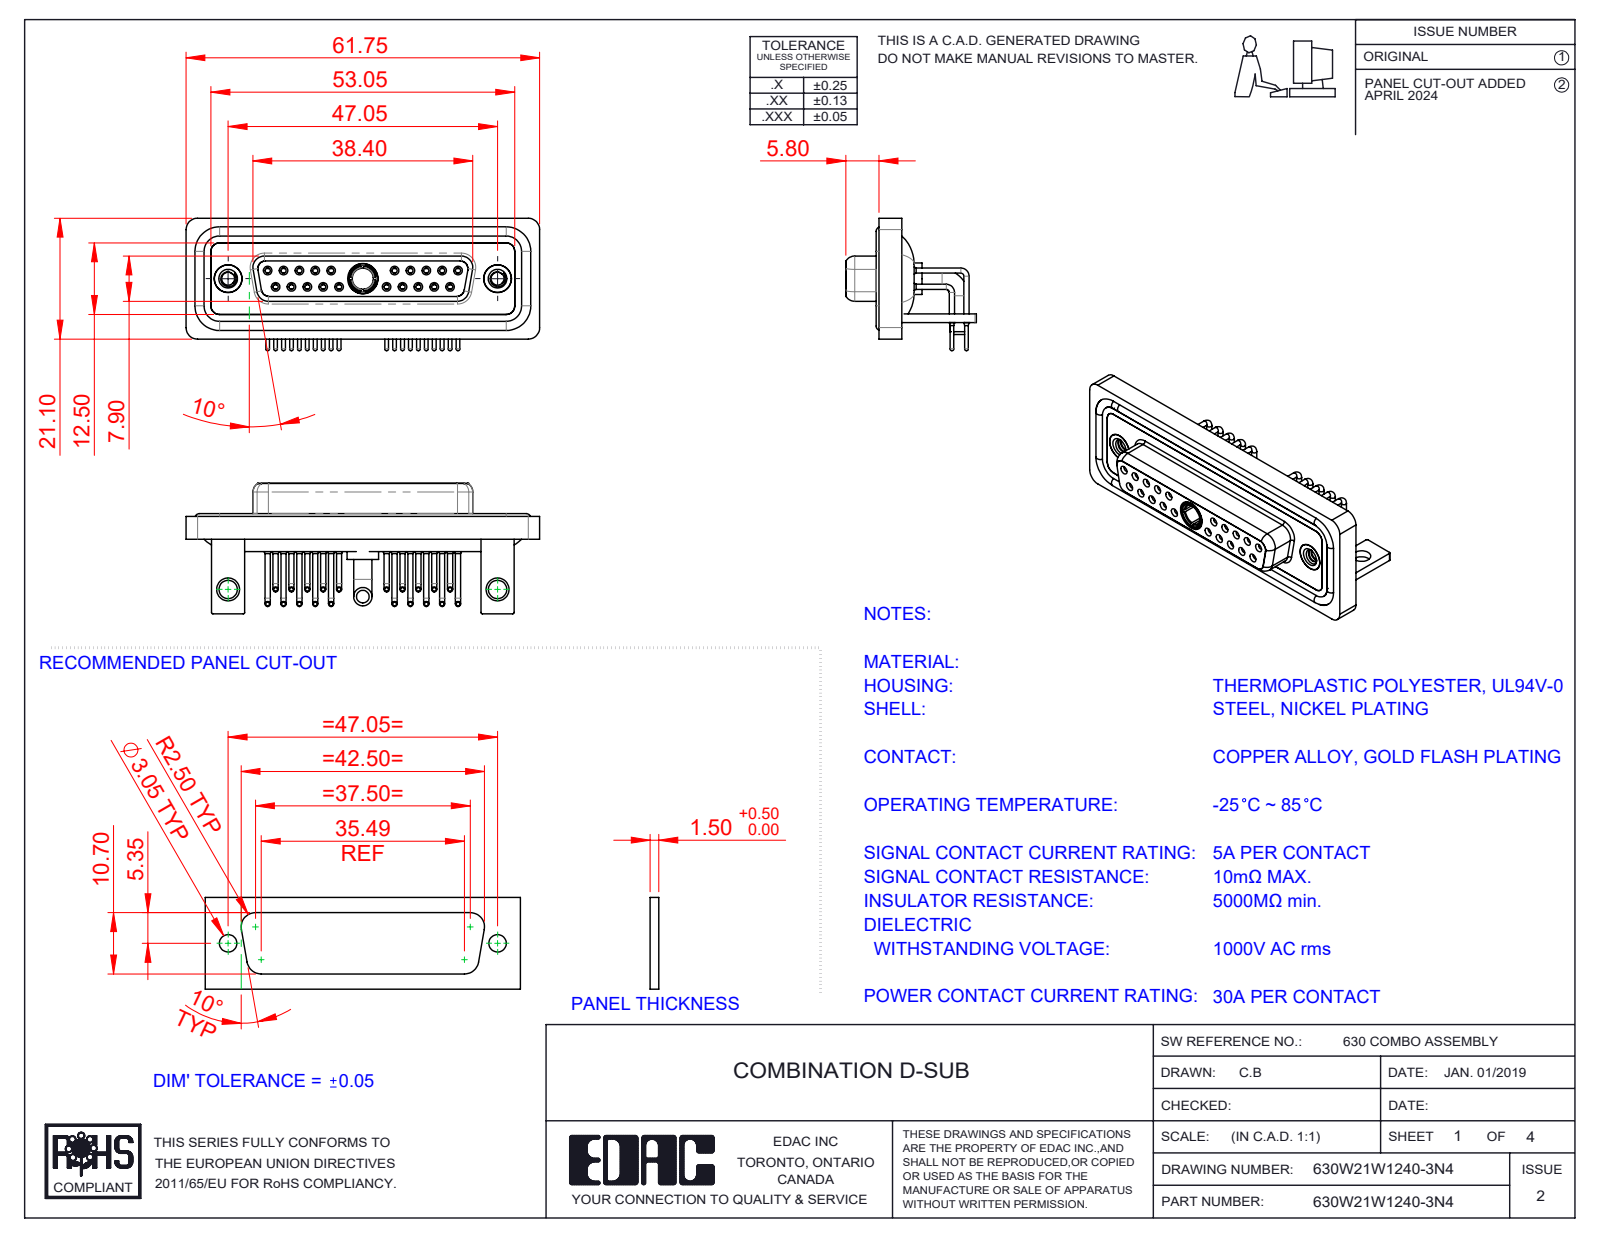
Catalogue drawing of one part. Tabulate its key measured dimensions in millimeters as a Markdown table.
| quantity | value |
| --- | --- |
| part name | 630Combo Contact Row 2_50 Contacts; 630Combo Waterproof Housing_25 Contacts; Power Socket_30A RA; 630Combo Housing_21W1 (+6 more) |
| STEP written by | SolidWorks 2023 (CONFIG_CONTROL_DESIGN) |
| units | millimeters |
| bodies | 31 solids, 1572 faces (454 planar, 697 cylindrical, 421 other) |
| overall size | 61.75 × 23.12 × 22.8 |
| volume | 8 900 mm³ |
| surface area | 15 533 mm² |
| round holes (diameter × count) | 0.9 × 20, 1.1 × 20, 1.5 × 20, 2 × 20, 1.6 × 10, 1.7 × 10, 4.85 × 3, 2.26 × 2, 3.2 × 2, 4 × 2, 4.05 × 2, 5 × 2 |
| round bosses / shafts (diameter × count) | 0.9 × 20, 0.65 × 20, 1.6 × 14, 4.95 × 2, 4.8 × 2, 3.2 × 2, 5.5 × 1, 5.2 × 1 |
| partial cylindrical surfaces (radius × count) | 2 × 19, 1.5 × 18, 0.25 × 16, 1.35 × 8, 1.6 × 8, 0.5 × 5, 0.6 × 4, 0.65 × 4 |
| main face-to-face distances | 0.4, 1.8, 2.9, 3.7, 1.5, 4.1, 1.1, 1.4, 1.6, 2.5 |
| hole center spacings | 3.16, 2.77, 5.54, 8.31, 5.04, 19.39, 20.97, 22.16 |
